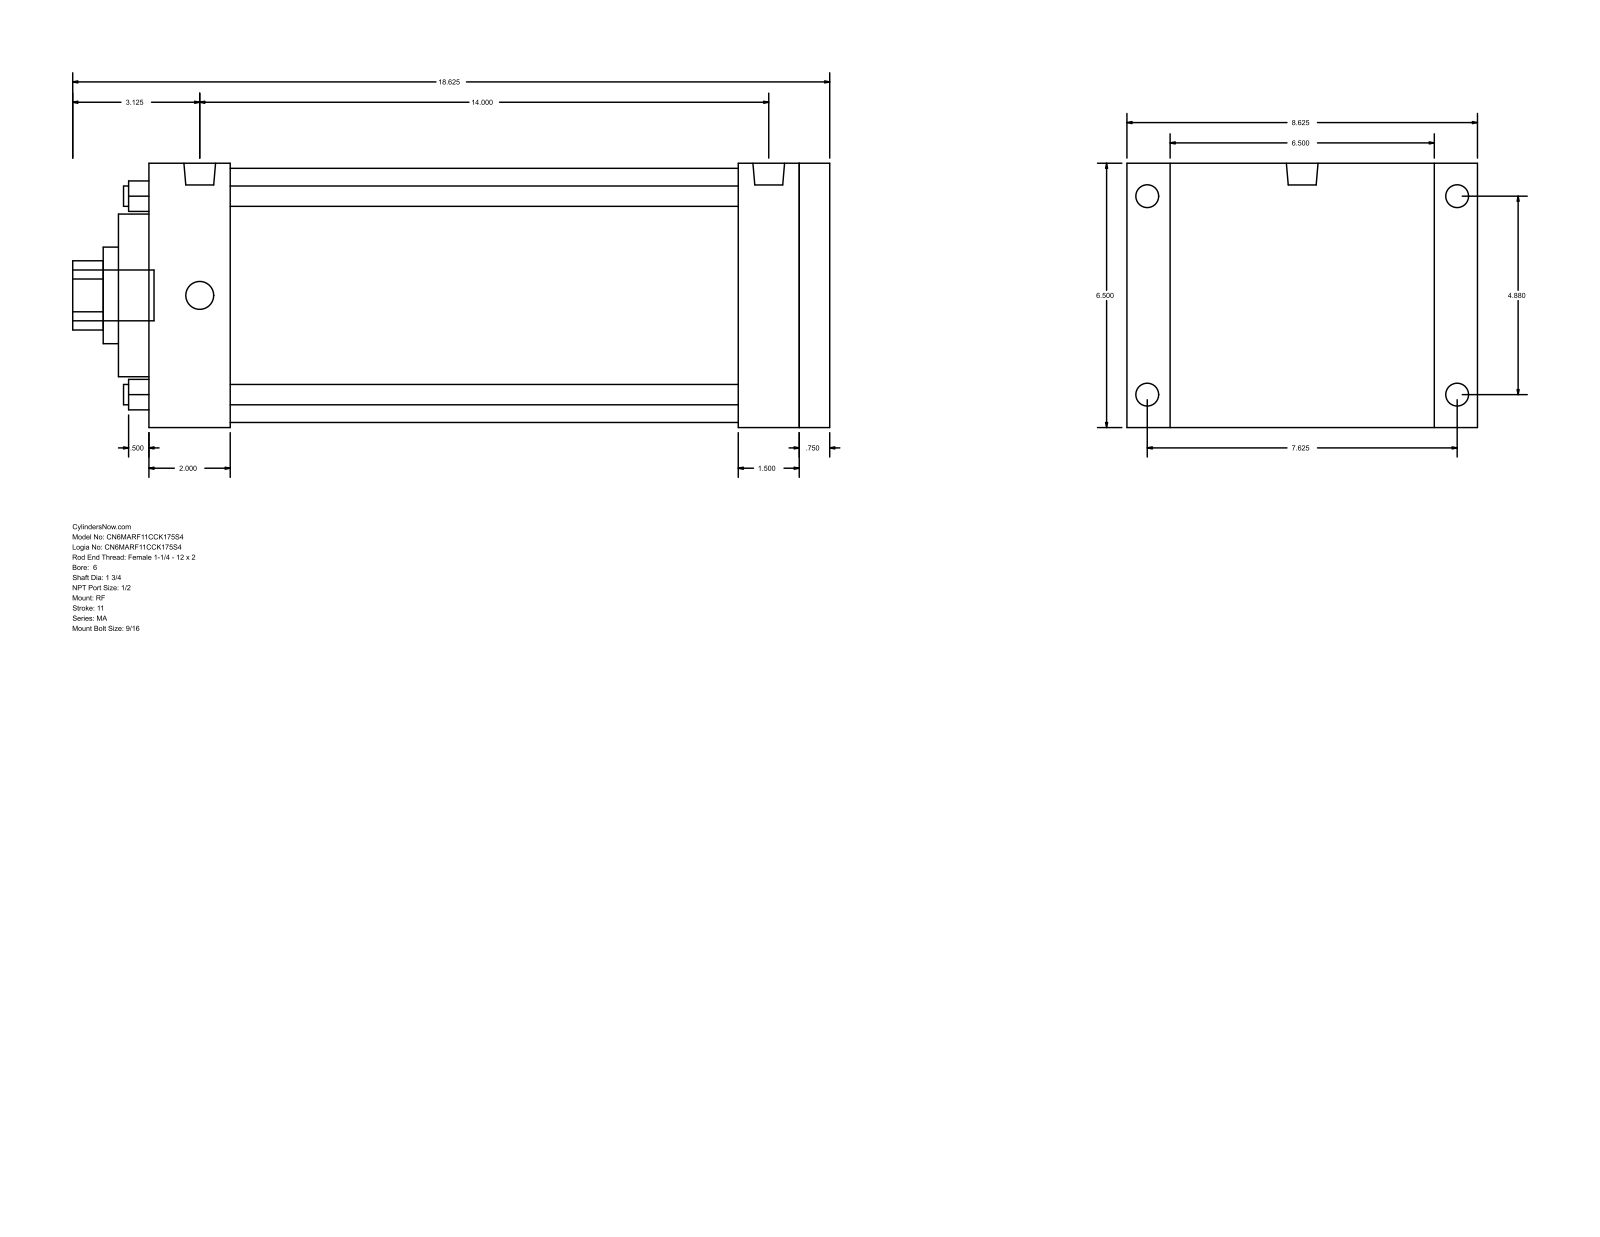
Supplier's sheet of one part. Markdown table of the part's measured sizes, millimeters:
| quantity | value |
| --- | --- |
| part name | MA_RF__0600_1.75 |
| STEP written by | GSSL Pune (CONFIG_CONTROL_DESIGN) |
| units | millimeters |
| bodies | 0 solids, 94 faces (65 planar, 29 cylindrical, 0 other) |
| overall size | 473.07 × 219.07 × 165.1 |
| round holes (diameter × count) | 12.7 × 4, 44.45 × 1, 60.33 × 1, 101.6 × 1, 158.75 × 1 |
| round bosses / shafts (diameter × count) | 17.46 × 4, 14.29 × 4, 19.77 × 2, 31.75 × 1 |
| partial cylindrical surfaces (radius × count) | 21.63 × 1 |
| main face-to-face distances | 165.1, 425.45, 19.05, 406.4, 50.8, 355.6, 374.65, 368.31, 317.51, 38.09 |
| hole center spacings | 87.65, 123.96, 175.31 |
